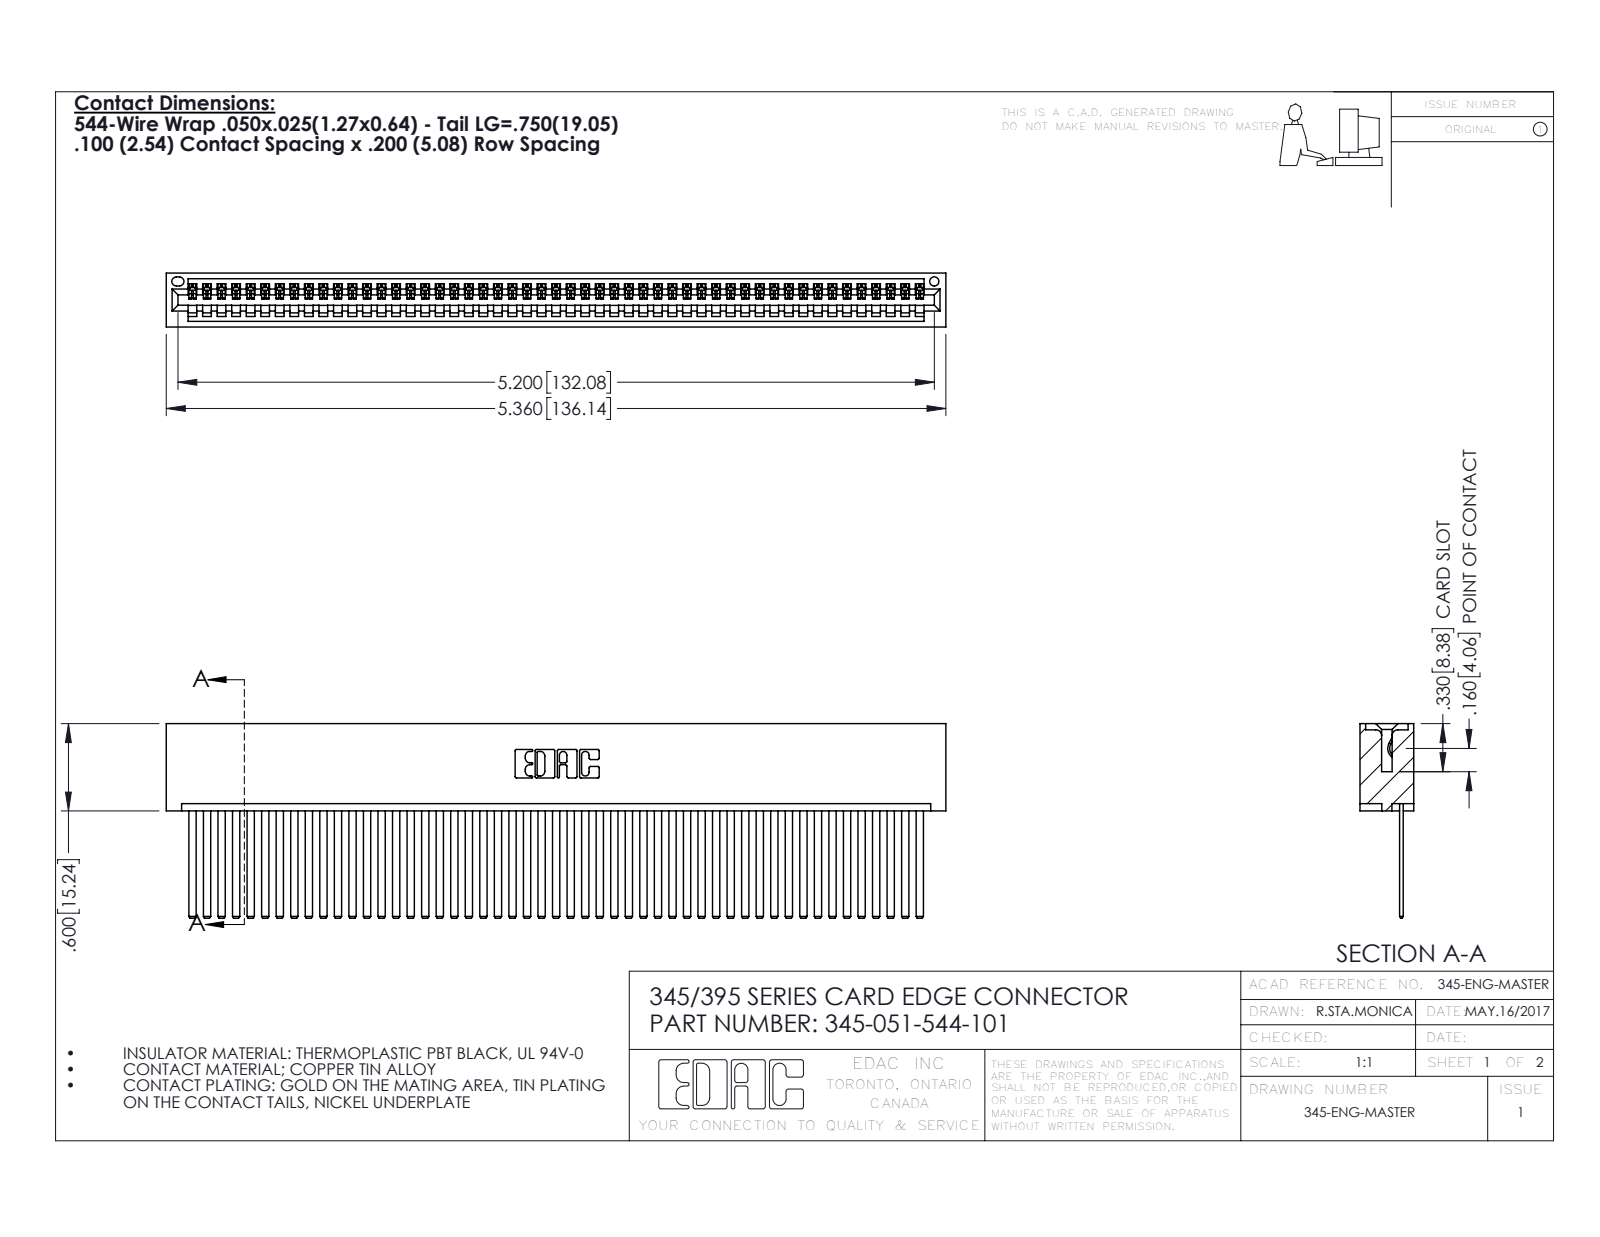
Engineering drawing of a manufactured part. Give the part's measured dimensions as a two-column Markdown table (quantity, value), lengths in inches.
| quantity | value |
| --- | --- |
| part name | 345-051-544-101; 345 Part_No Mounting Lugs; 345-292-001_345-293-144 |
| STEP written by | SolidWorks 2016 (CONFIG_CONTROL_DESIGN) |
| units | inches |
| bodies | 52 solids, 2770 faces (1912 planar, 858 cylindrical, 0 other) |
| overall size | 5.36 × 1.337 × 0.37 |
| volume | 0.865 in³ |
| surface area | 32.44 in² |
| round holes (diameter × count) | 0.064 × 1 |
| partial cylindrical surfaces (radius × count) | 0.006 × 102, 0.01 × 22, 0.007 × 6, 0.031 × 6, 0.026 × 3, 0.031 × 2, 0.04 × 2, 0.014 × 1 |
| main face-to-face distances | 0.072, 0.298, 0.025, 0.098, 0.272, 0.37, 0.2, 0.225, 0.149, 0.072 |
